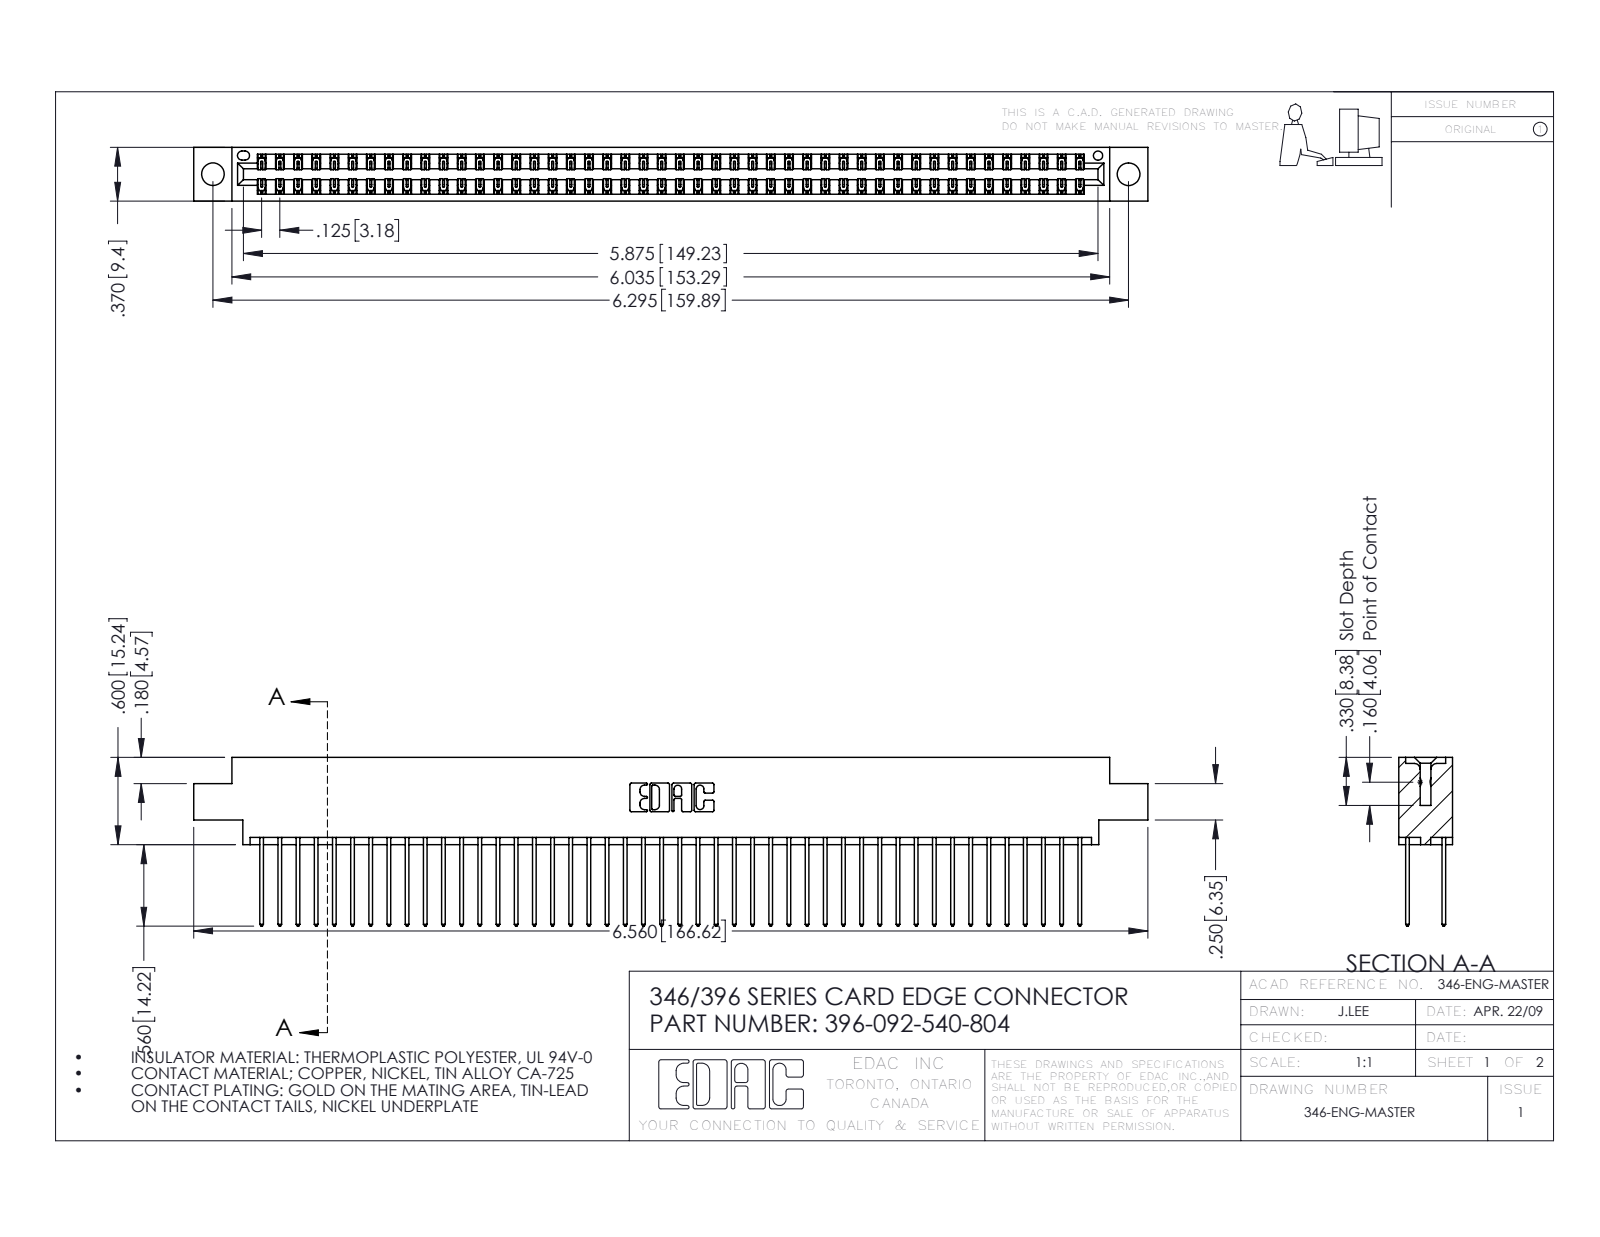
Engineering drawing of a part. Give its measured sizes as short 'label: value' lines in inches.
name: 396-092-540-804; 346 Part_0.170 Offset - 0.156 Dia-TH; 345-292-001_345-293-140
written by: SolidWorks 2016 (CONFIG_CONTROL_DESIGN)
unit: in
bodies: 93 solids, 4910 faces (3300 planar, 1610 cylindrical, 0 other)
size: 6.56 × 1.16 × 0.37
volume: 1 in³; area: 37.55 in²
holes: 2× ⌀0.156, 1× ⌀0.064
rounds: 138× R0.006, 92× R0.01, 22× R0.01, 6× R0.007, 6× R0.031, 3× R0.026, 2× R0.014, 2× R0.022
face distances: 0.048, 0.322, 0.25, 0.072, 0.298, 0.025, 0.37, 0.275, 0.148, 0.222
hole spacings: 0.246, 6.086, 6.295
